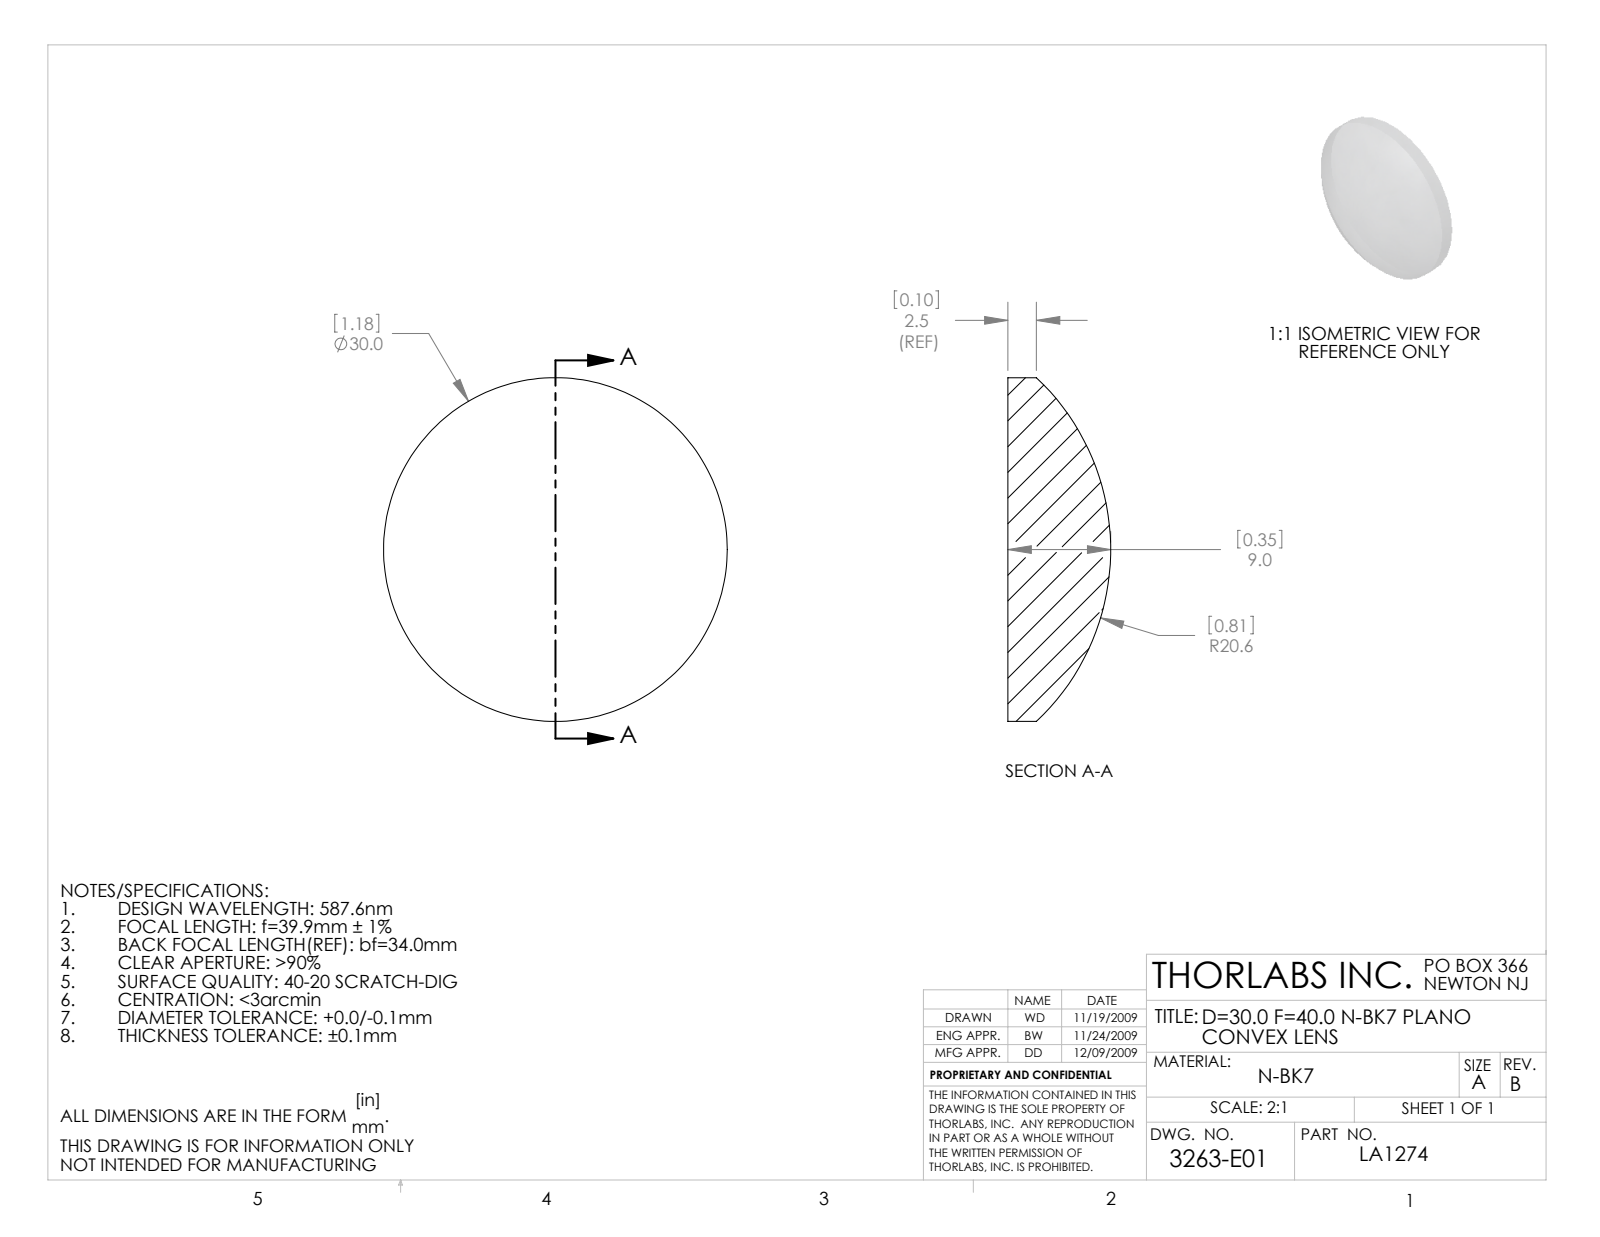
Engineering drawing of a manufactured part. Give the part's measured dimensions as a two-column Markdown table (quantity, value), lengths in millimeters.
| quantity | value |
| --- | --- |
| part name | 3263-E0W |
| STEP written by | SolidWorks 2009 (AUTOMOTIVE_DESIGN) |
| units | millimeters |
| bodies | 1 solid, 5 faces (1 planar, 2 cylindrical, 2 other) |
| overall size | 30 × 30 × 8.97 |
| volume | 4 193 mm³ |
| surface area | 1 780 mm² |
| round bosses / shafts (diameter × count) | 30 × 1 |
